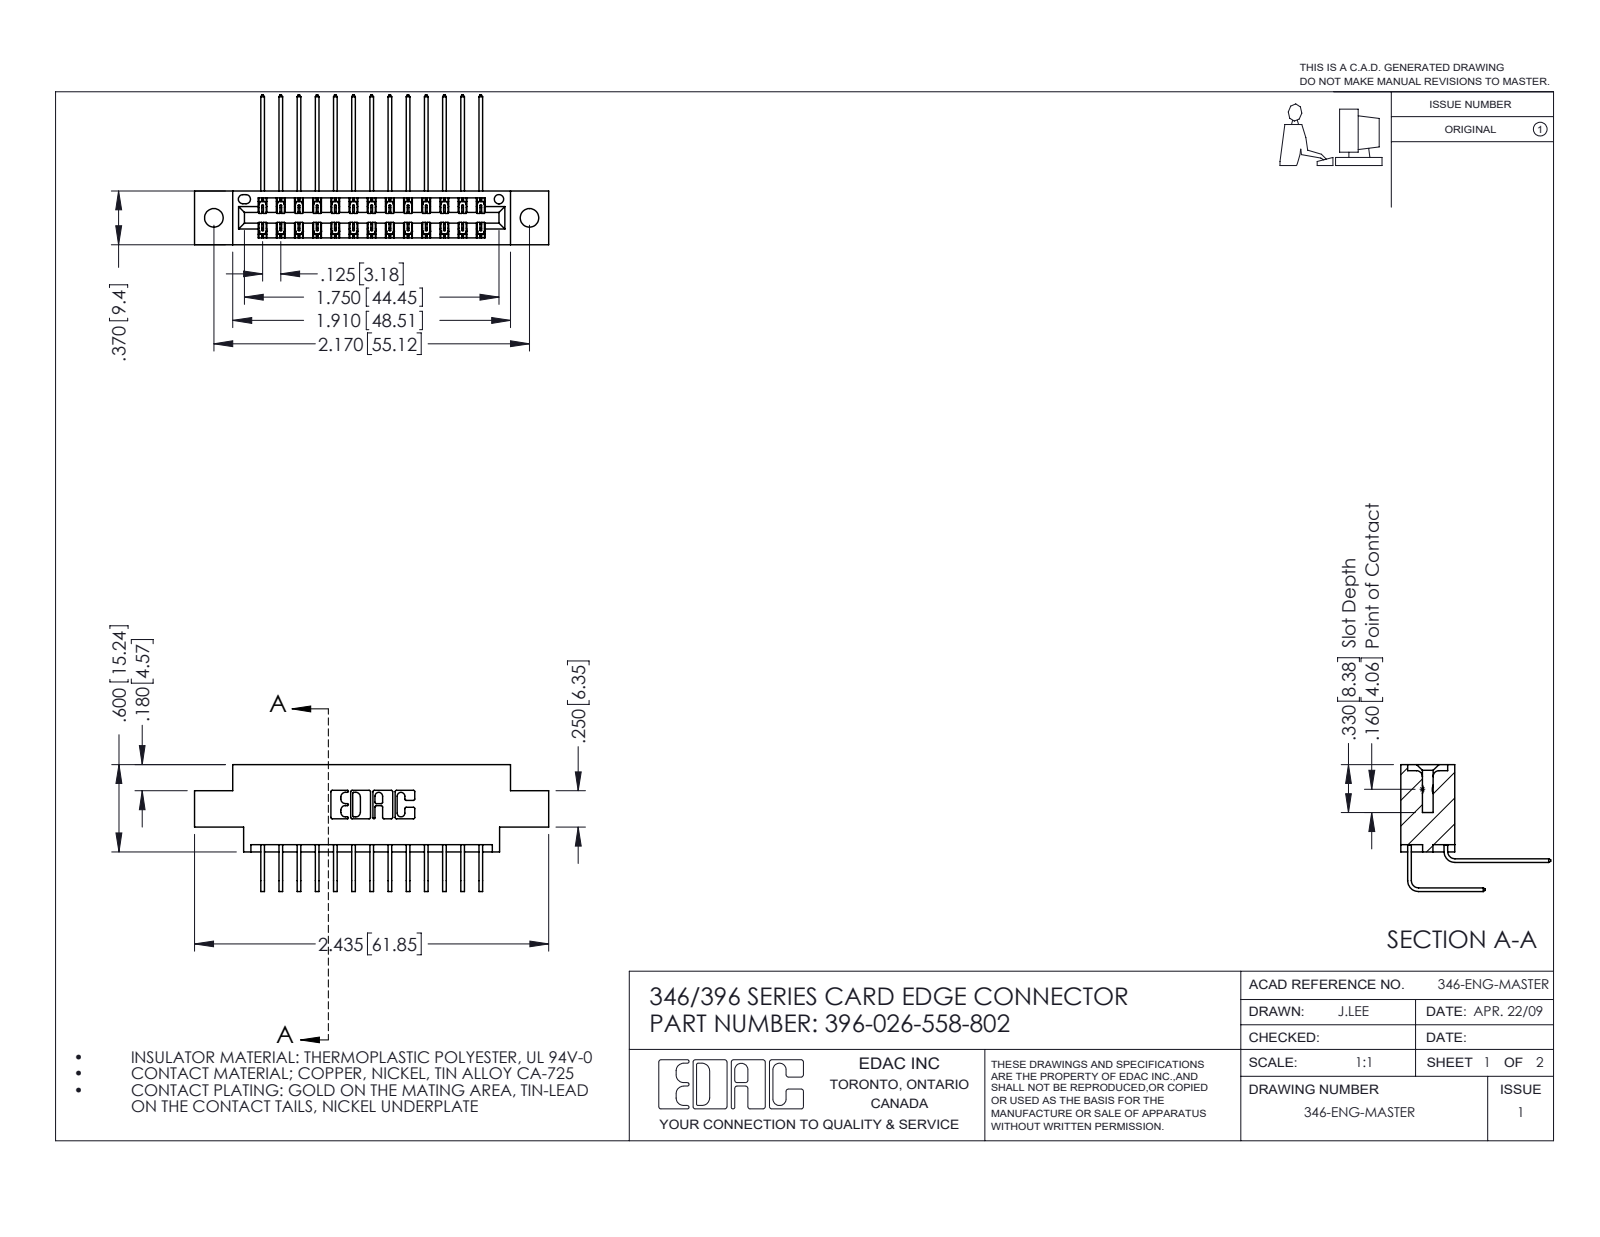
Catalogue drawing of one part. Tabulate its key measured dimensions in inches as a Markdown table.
| quantity | value |
| --- | --- |
| part name | 345-292-001_558 Tail - 2; 346 Part_0.170 Offset - 0.128 Dia; 396-026-558-802; 345-292-001_558 559 Tail - 1 |
| STEP written by | SolidWorks 2016 (CONFIG_CONTROL_DESIGN) |
| units | inches |
| bodies | 27 solids, 1530 faces (1042 planar, 488 cylindrical, 0 other) |
| overall size | 2.435 × 1.03 × 0.873 |
| volume | 0.352 in³ |
| surface area | 12.55 in² |
| round holes (diameter × count) | 0.128 × 2, 0.064 × 1 |
| partial cylindrical surfaces (radius × count) | 0.006 × 39, 0.01 × 22, 0.007 × 6, 0.031 × 6, 0.026 × 3, 0.014 × 2, 0.022 × 2, 0.024 × 2 |
| main face-to-face distances | 0.048, 0.322, 0.25, 0.37, 0.025, 0.072, 0.298, 0.275, 0.148, 0.222 |
| hole center spacings | 0.246, 1.964, 2.17 |
